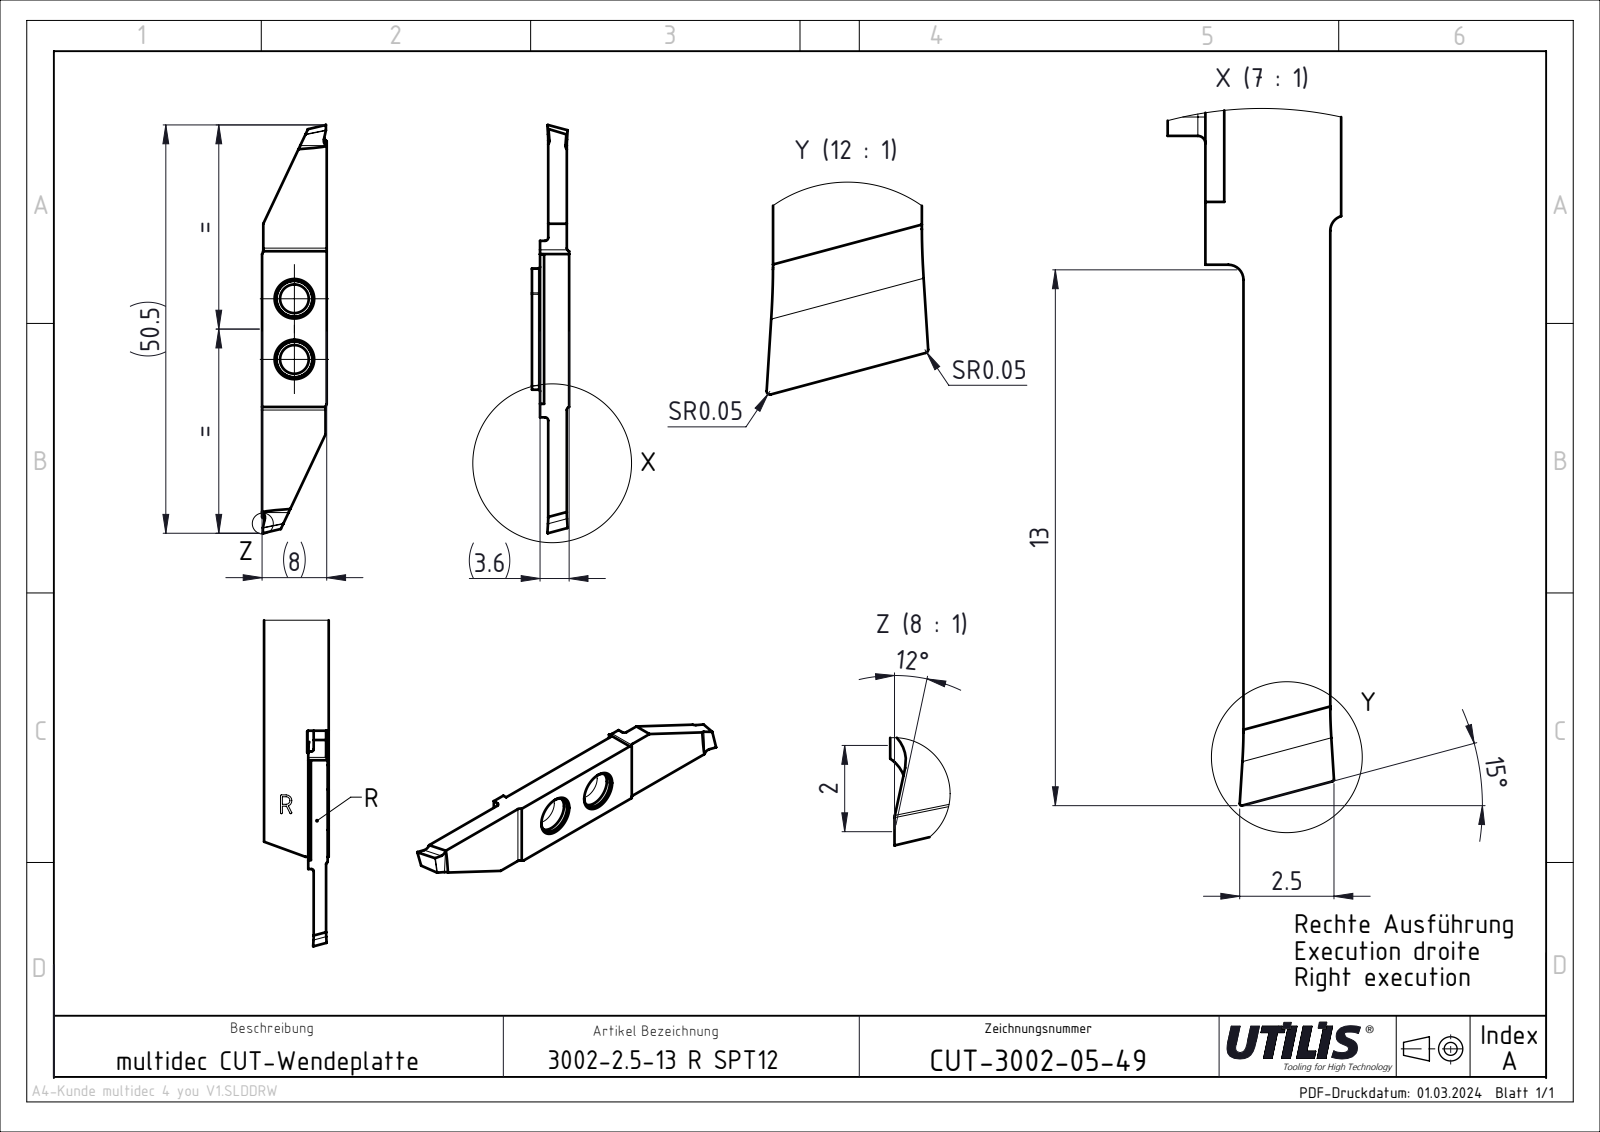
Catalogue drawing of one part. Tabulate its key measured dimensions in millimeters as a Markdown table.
| quantity | value |
| --- | --- |
| part name | CUT-3002 SPT Slim_and_Deep; ASME Y14.5 |
| STEP written by | SolidWorks 2023 SP4 \|\| FormatWorks Professional (AP242_MANAGED_MODEL_BASED_3D_ENGINEERING_MIM_LF) |
| units | millimeters |
| bodies | 1 solid, 40 faces (26 planar, 14 cylindrical, 0 other) |
| overall size | 50.5 × 8 × 3.6 |
| volume | 900 mm³ |
| surface area | 1 003 mm² |
| round holes (diameter × count) | 3.55 × 2 |
| partial cylindrical surfaces (radius × count) | 0.4 × 4, 1 × 2 |
| main face-to-face distances | 2.3, 1.01, 3.31, 3.6, 2.59, 8, 18.09, 7.85, 7.7, 21.82 |
| hole center spacings | 7.5 |
